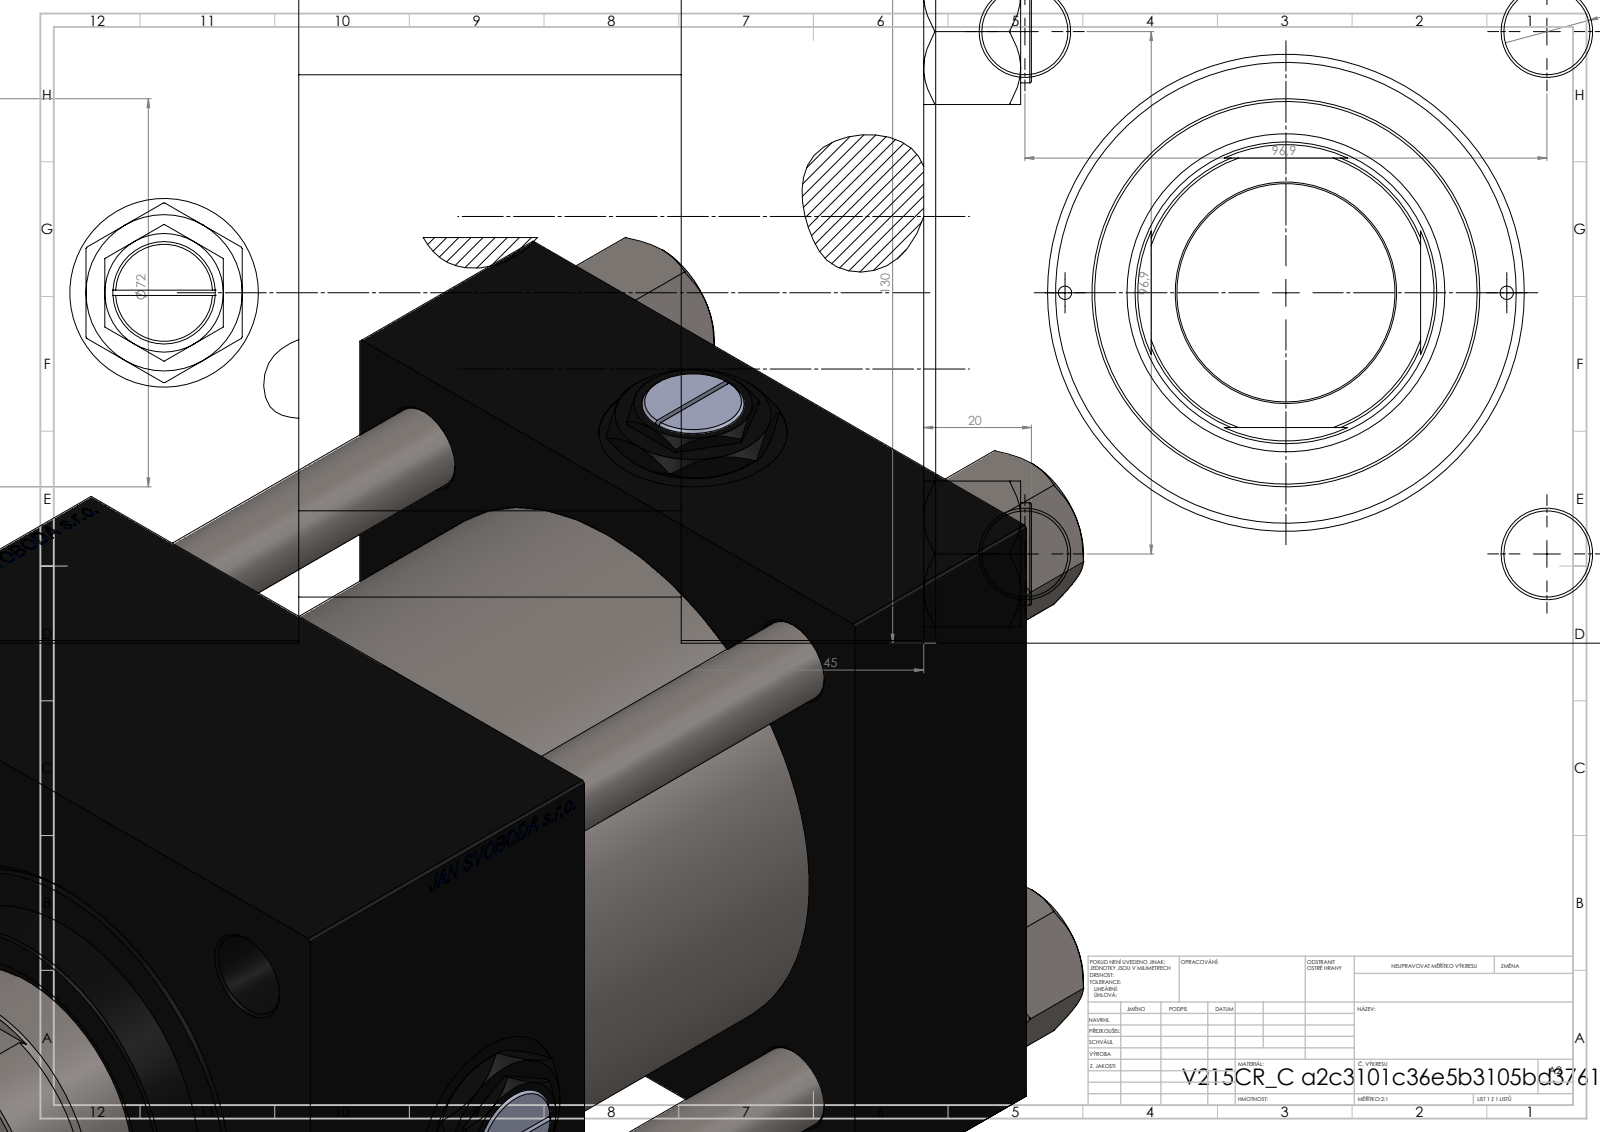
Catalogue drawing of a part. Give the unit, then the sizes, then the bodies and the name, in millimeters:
Units: millimetres
Overall size (bounding box): 243 × 137 × 137
Round holes (diameter × count): ⌀16 ×4, ⌀2.5 ×2, ⌀7 ×2, ⌀26.44 ×2, ⌀35 ×2, ⌀40.5 ×1, ⌀56 ×1, ⌀59 ×1, ⌀76 ×1, ⌀85.5 ×1, ⌀100 ×1
Round bosses / shafts (diameter × count): ⌀19 ×4, ⌀106 ×1, ⌀72 ×1
Partial cylindrical surfaces — rounded edges, fillets, slot ends (radius × count): R27 ×1
Main face-to-face distances: 130, 45, 188, 143, 116, 71, 72, 20, 51, 92
Hole centre spacings: 49.02, 68.52, 96.9, 101.73, 41, 137.04, 82
Volume: 2 460 000 mm³ · Surface area: 340 663 mm²
Bodies: 13 solids, 1303 faces (623 planar, 102 cylindrical, 578 other)
Part name (STEP PRODUCT): V215CR_C_TYCINKA; V215CR_C_Body; V215_VC_A; V215CR_VCP_C (+2 more)
STEP written by: SolidWorks 2019 (CONFIG_CONTROL_DESIGN)
